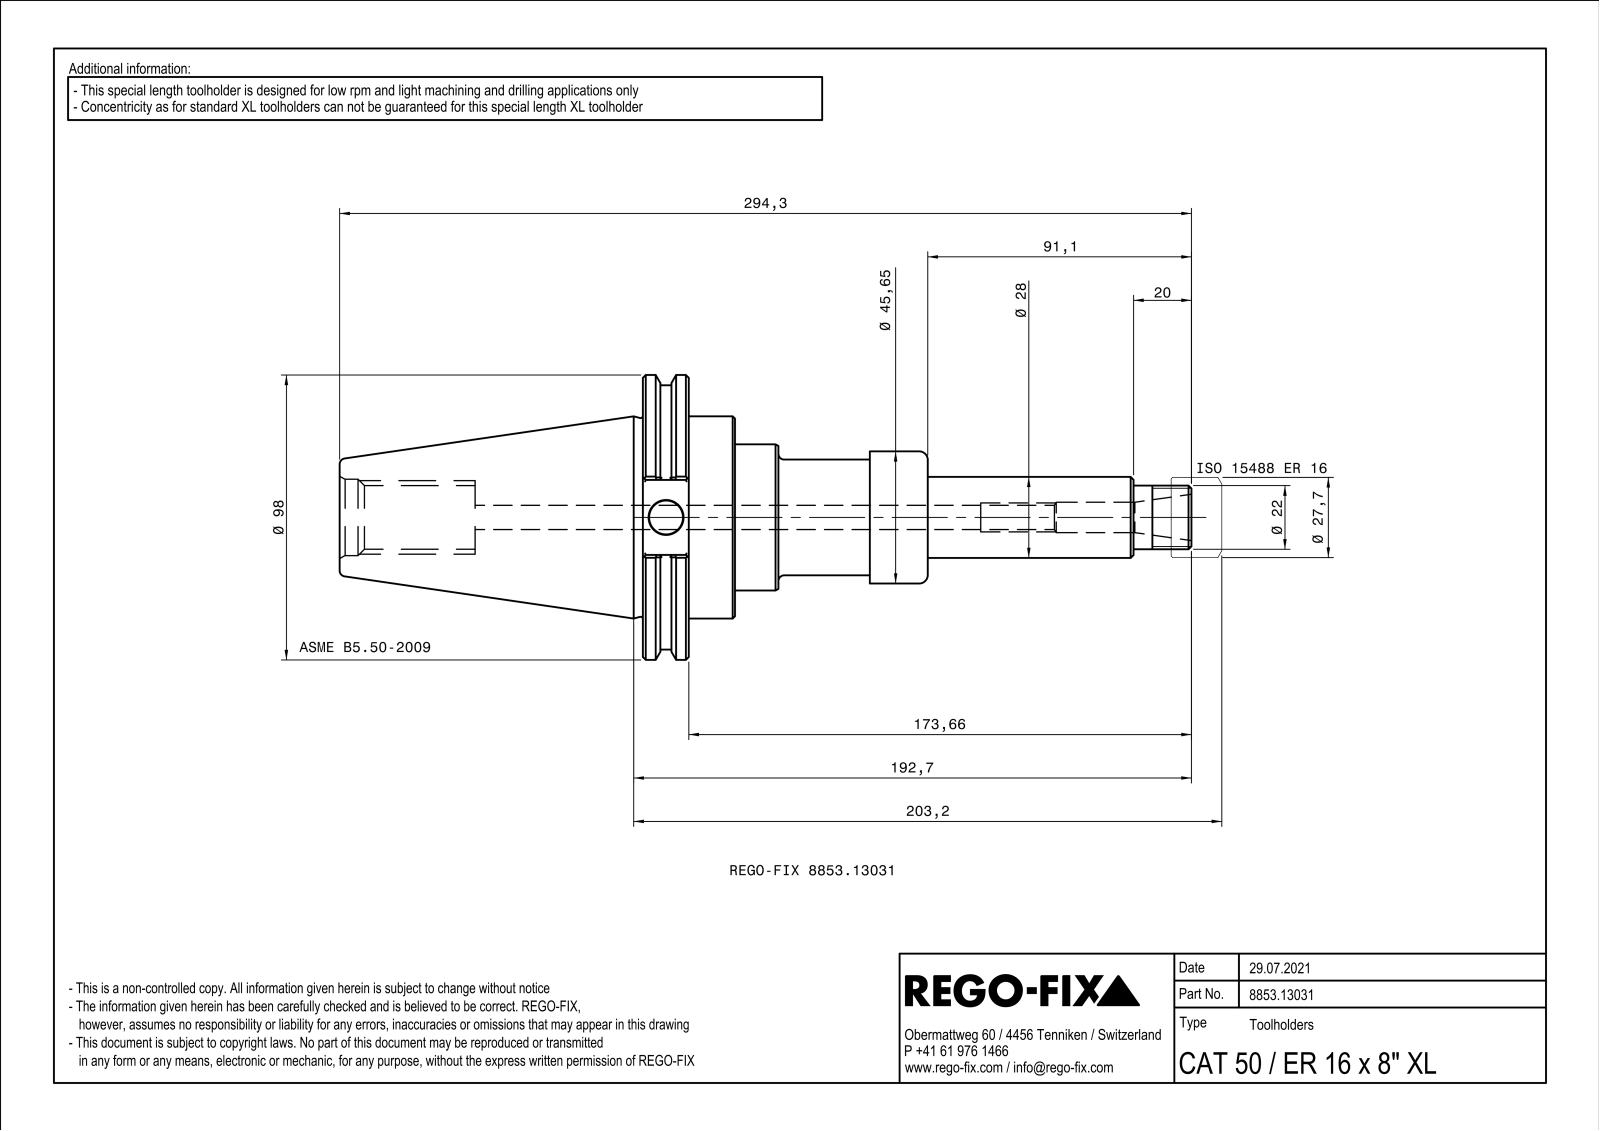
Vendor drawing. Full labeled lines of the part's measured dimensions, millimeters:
Part name (STEP PRODUCT): NOCUT
STEP written by: SIEMENS PLM Software Solid Edge ST10 (AUTOMOTIVE_DESIGN)
Units: millimetres
Bodies: 1 solid, 152 faces (43 planar, 40 cylindrical, 69 other)
Overall size (bounding box): 294.3 × 98.42 × 94.39
Volume: 504 804 mm³ · Surface area: 77 806 mm²
Round holes (diameter × count): ⌀8.35 ×1, ⌀8.38 ×1, ⌀10 ×1, ⌀10.5 ×1, ⌀11.7 ×1, ⌀21.96 ×1, ⌀25 ×1, ⌀26.4 ×1, ⌀29 ×1, ⌀38.38 ×1, ⌀40.05 ×1, ⌀43.3 ×1
Round bosses / shafts (diameter × count): ⌀98.42 ×1, ⌀91.3 ×1, ⌀69.85 ×1, ⌀50.5 ×1, ⌀45.65 ×1, ⌀40 ×1, ⌀34 ×1, ⌀33 ×1
Partial cylindrical surfaces — rounded edges, fillets, slot ends (radius × count): R0.5 ×12
Main face-to-face distances: 15.87, 15.96, 31.83, 66.6, 82.56, 98.43, 6, 14, 203.2, 136.6
